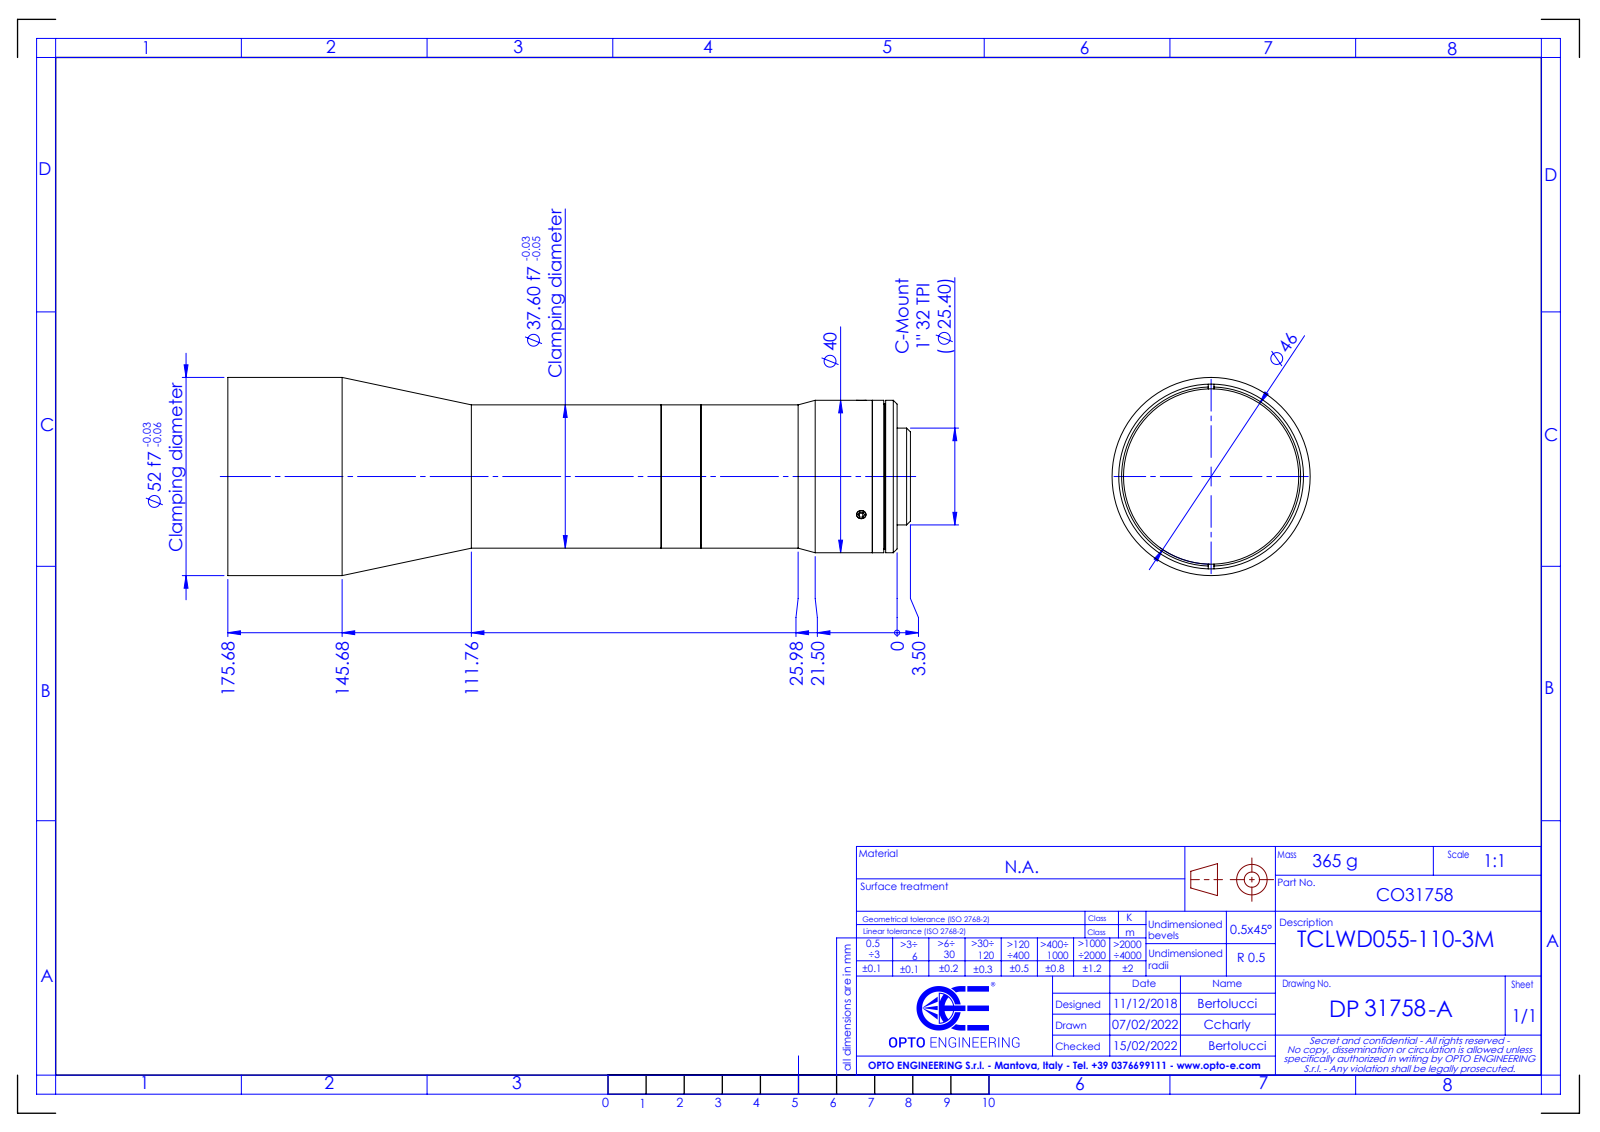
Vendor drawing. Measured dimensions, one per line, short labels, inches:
name: DP31758-A_TCLWD055-110-3M
written by: SolidWorks 2021 (CONFIG_CONTROL_DESIGN)
unit: in
bodies: 0 solids, 85 faces (40 planar, 26 cylindrical, 19 other)
size: 7.054 × 2.047 × 2.047
holes: 1× ⌀0.886, 1× ⌀1.004, 1× ⌀1.26, 1× ⌀1.811, 1× ⌀1.909
bosses: 1× ⌀2.047, 1× ⌀1.575, 1× ⌀1.48, 1× ⌀1
face distances: 0.138, 0.118, 0.02, 0.256, 1.769, 1.887, 1.907, 2.025, 4.892, 6.661
